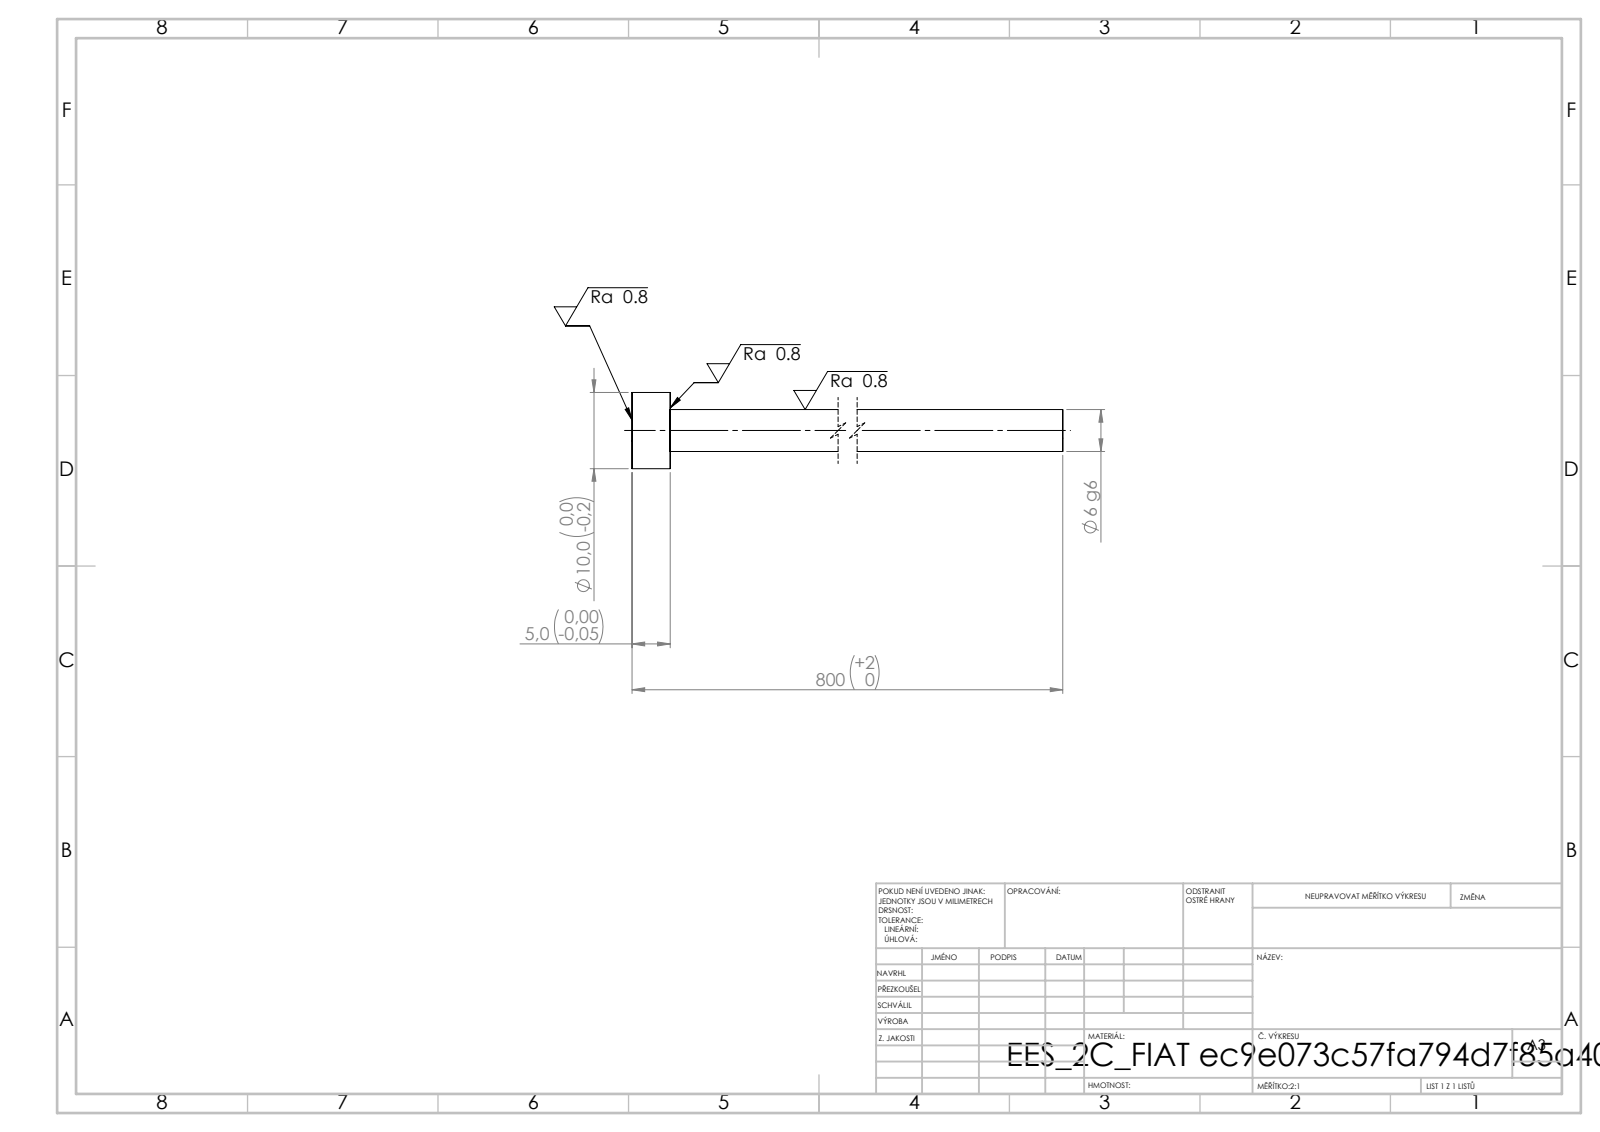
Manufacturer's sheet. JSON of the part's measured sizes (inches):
{"step_written_by": "SolidWorks 2019 (CONFIG_CONTROL_DESIGN)", "units": "inches", "bodies": {"solids": 1, "faces": 7, "planar": 3, "cylindrical": 4, "other": 0}, "overall_size": [31.496, 0.394, 0.394], "volume_in3": 1.177, "surface_area_in2": 21.78, "round_bosses_or_shafts": [[0.394, 1], [0.217, 1]], "face_to_face_distances": [0.197, 31.496, 31.299]}
